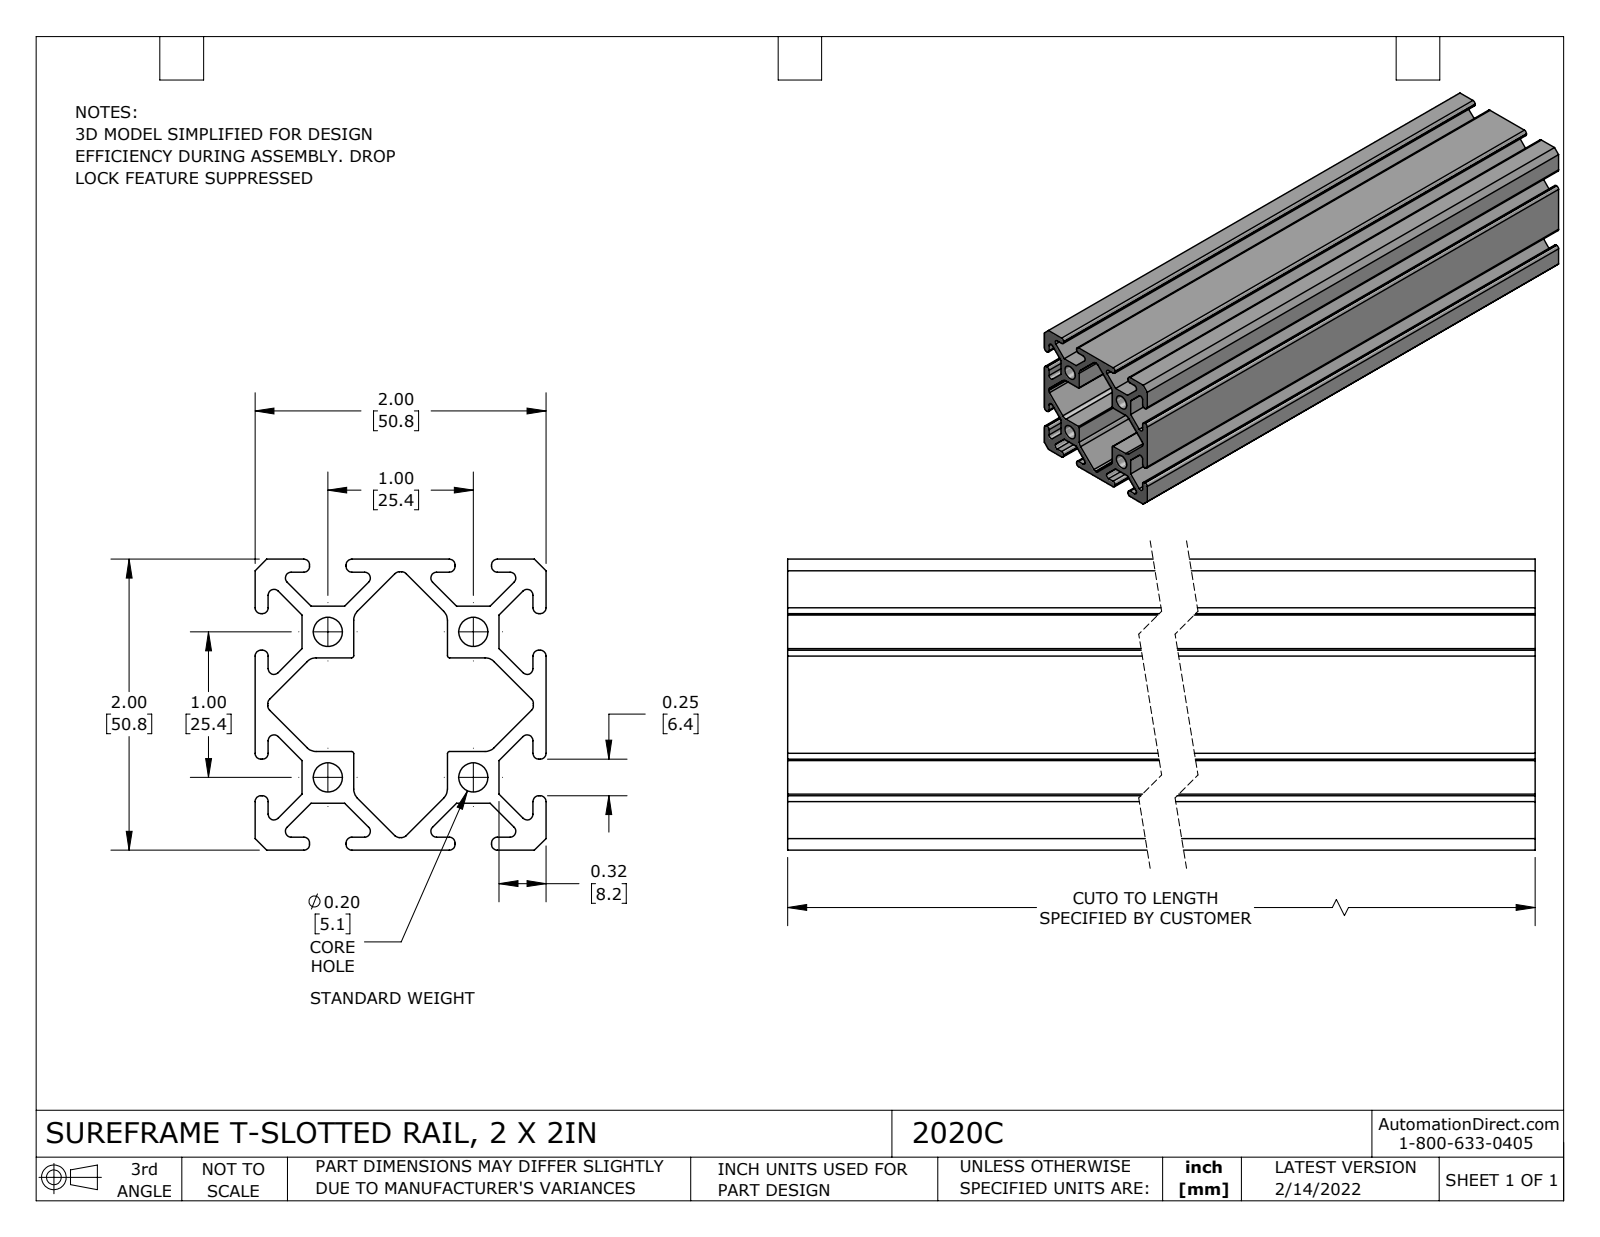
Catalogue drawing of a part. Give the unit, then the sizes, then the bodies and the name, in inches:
Units: inches
Overall size (bounding box): 8 × 2 × 2
Round holes (diameter × count): ⌀0.201 ×4
Partial cylindrical surfaces — rounded edges, fillets, slot ends (radius × count): R0.04 ×48, R0.087 ×24, R0.044 ×8, R0.015 ×4
Main face-to-face distances: 2, 0.678, 1.322, 0.087, 1.414, 0.707, 0.794, 0.62, 0.707, 1.327
Hole centre spacings: 1, 1.414
Volume: 10.02 in³ · Surface area: 195.5 in²
Bodies: 1 solid, 194 faces (94 planar, 100 cylindrical, 0 other)
Part name (STEP PRODUCT): 2020C
STEP written by: SolidWorks 2021 (CONFIG_CONTROL_DESIGN)
